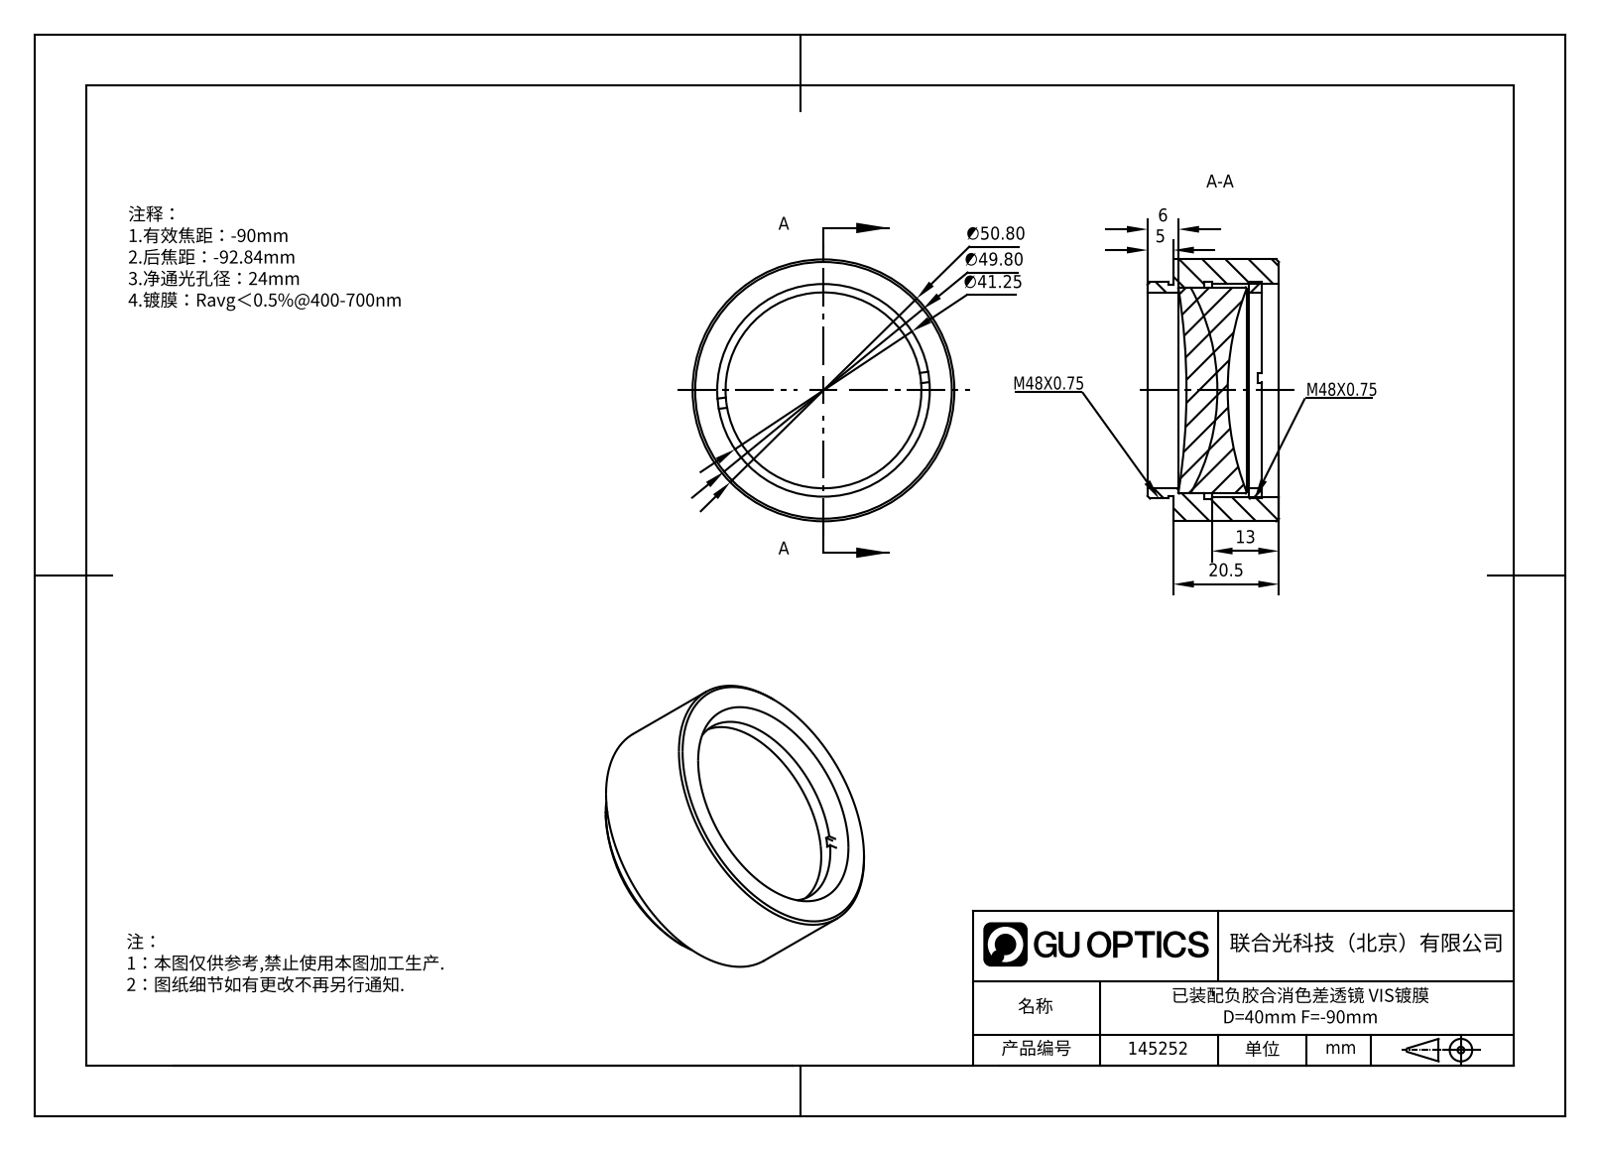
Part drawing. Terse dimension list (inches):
name: GL32-040-090-VIS_Solidworks; AND-ML40-090-VIS-A; M42x0.75安装环PN35012-LM400-D2; M42x0.75ѹȦ
written by: SolidWorks 2022 (AUTOMOTIVE_DESIGN)
unit: in
bodies: 4 solids, 56 faces (16 planar, 22 cylindrical, 18 other)
size: 2 × 2 × 1.004
volume: 1.821 in³; area: 26.5 in²
holes: 1× ⌀1.496, 1× ⌀1.624, 1× ⌀1.657
bosses: 1× ⌀2, 1× ⌀1.654, 1× ⌀1.614, 1× ⌀1.575
face distances: 0.807, 0.197, 0.236, 0.676, 0.131, 0.577, 0.098, 0.23, 0.039, 0.774
